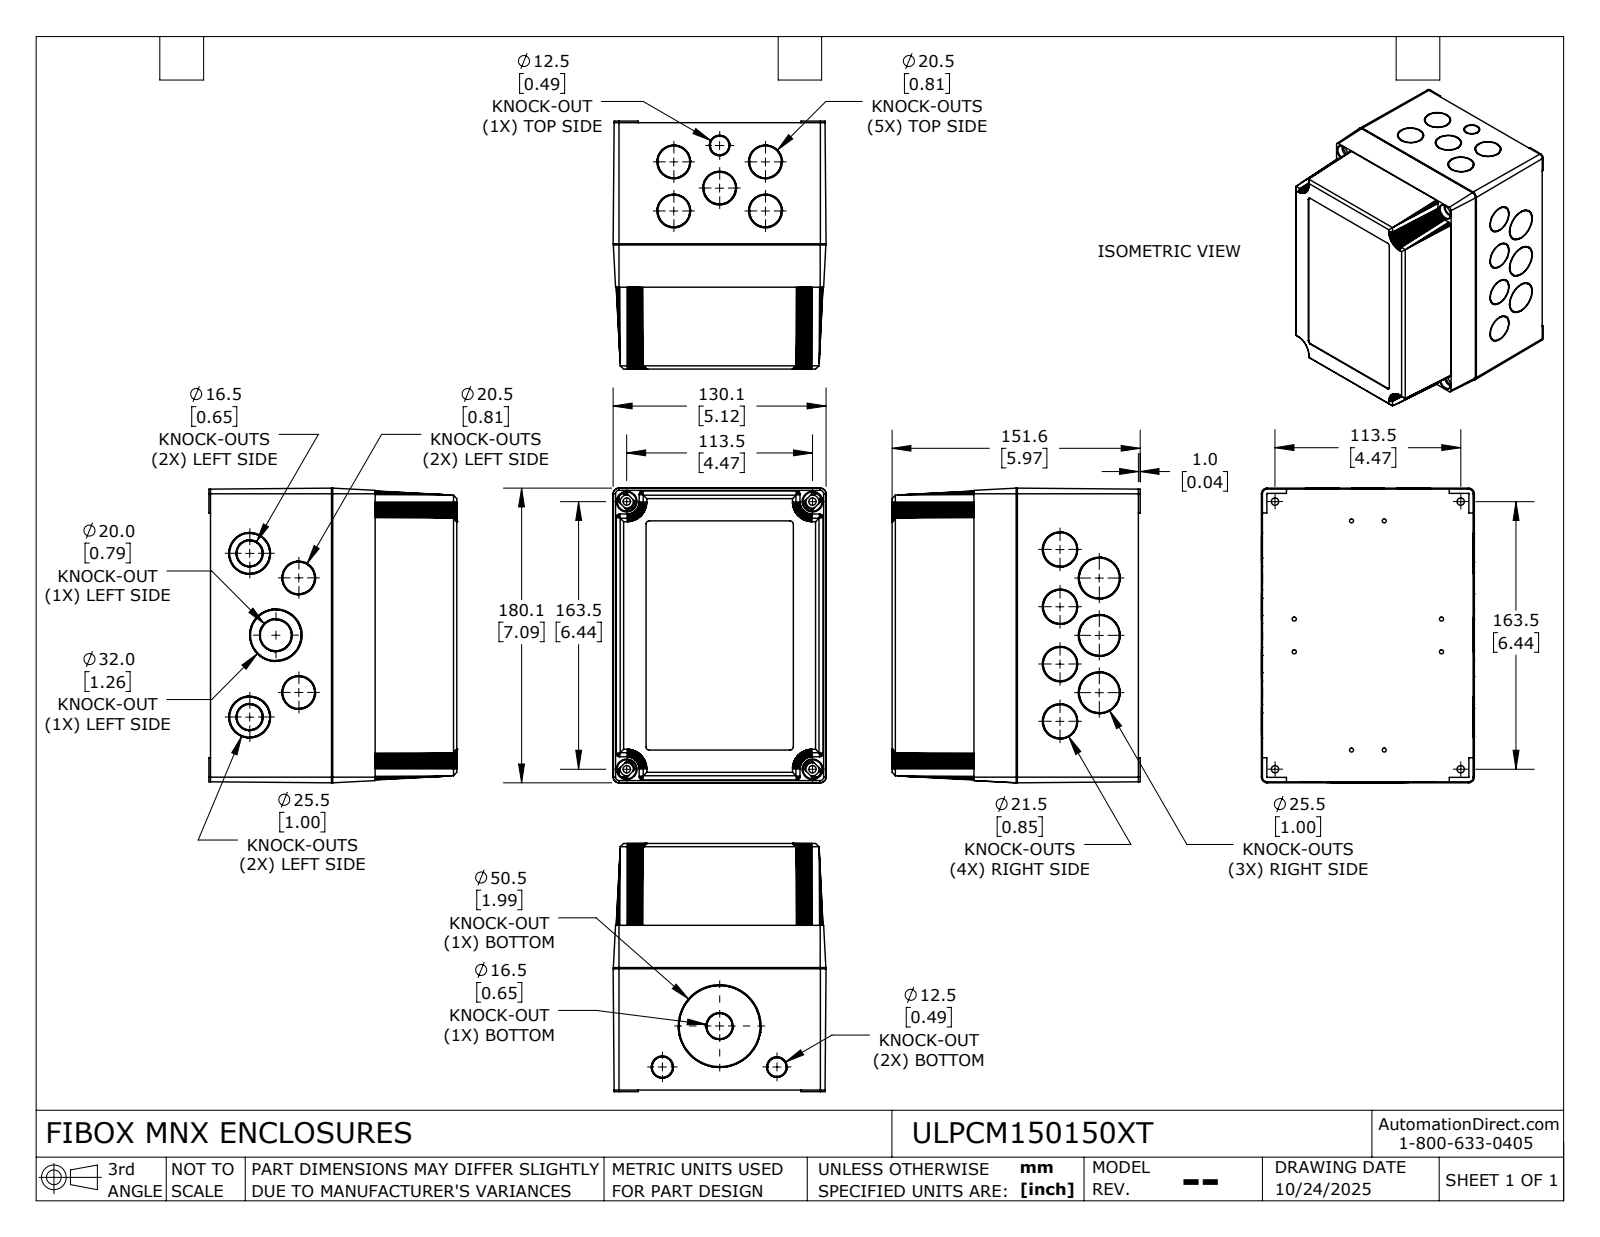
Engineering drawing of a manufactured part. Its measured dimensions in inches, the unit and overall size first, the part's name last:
Units: inches
Overall size (bounding box): 7.09 × 5.969 × 5.122
Round holes (diameter × count): ⌀0.098 ×8, ⌀0.126 ×8, ⌀0.807 ×7, ⌀1.004 ×5, ⌀0.177 ×4, ⌀0.315 ×4, ⌀0.456 ×4, ⌀0.846 ×4, ⌀0.65 ×3, ⌀0.492 ×1, ⌀0.531 ×1, ⌀0.787 ×1
Round bosses / shafts (diameter × count): ⌀0.315 ×8, ⌀0.768 ×7, ⌀0.965 ×5, ⌀0.807 ×4, ⌀0.61 ×3, ⌀0.453 ×2, ⌀1.949 ×1, ⌀1.22 ×1
Partial cylindrical surfaces — rounded edges, fillets, slot ends (radius × count): R0.051 ×8, R0.008 ×4, R0.079 ×4, R0.083 ×4, R0.108 ×4, R0.112 ×4, R0.191 ×4, R0.217 ×4
Main face-to-face distances: 0.166, 0.165, 5.646, 5.811, 0.015, 0.098, 5.744, 5.909, 4.6, 0.02
Hole centre spacings: 0.394, 1.169, 1.378, 2.756, 3.543, 0.787, 1.333, 1.575
Volume: 34.93 in³ · Surface area: 425.8 in²
Bodies: 2 solids, 1187 faces (991 planar, 160 cylindrical, 36 other)
Part name (STEP PRODUCT): ULPCM150150XT
STEP written by: SolidWorks 2024 (AUTOMOTIVE_DESIGN)
